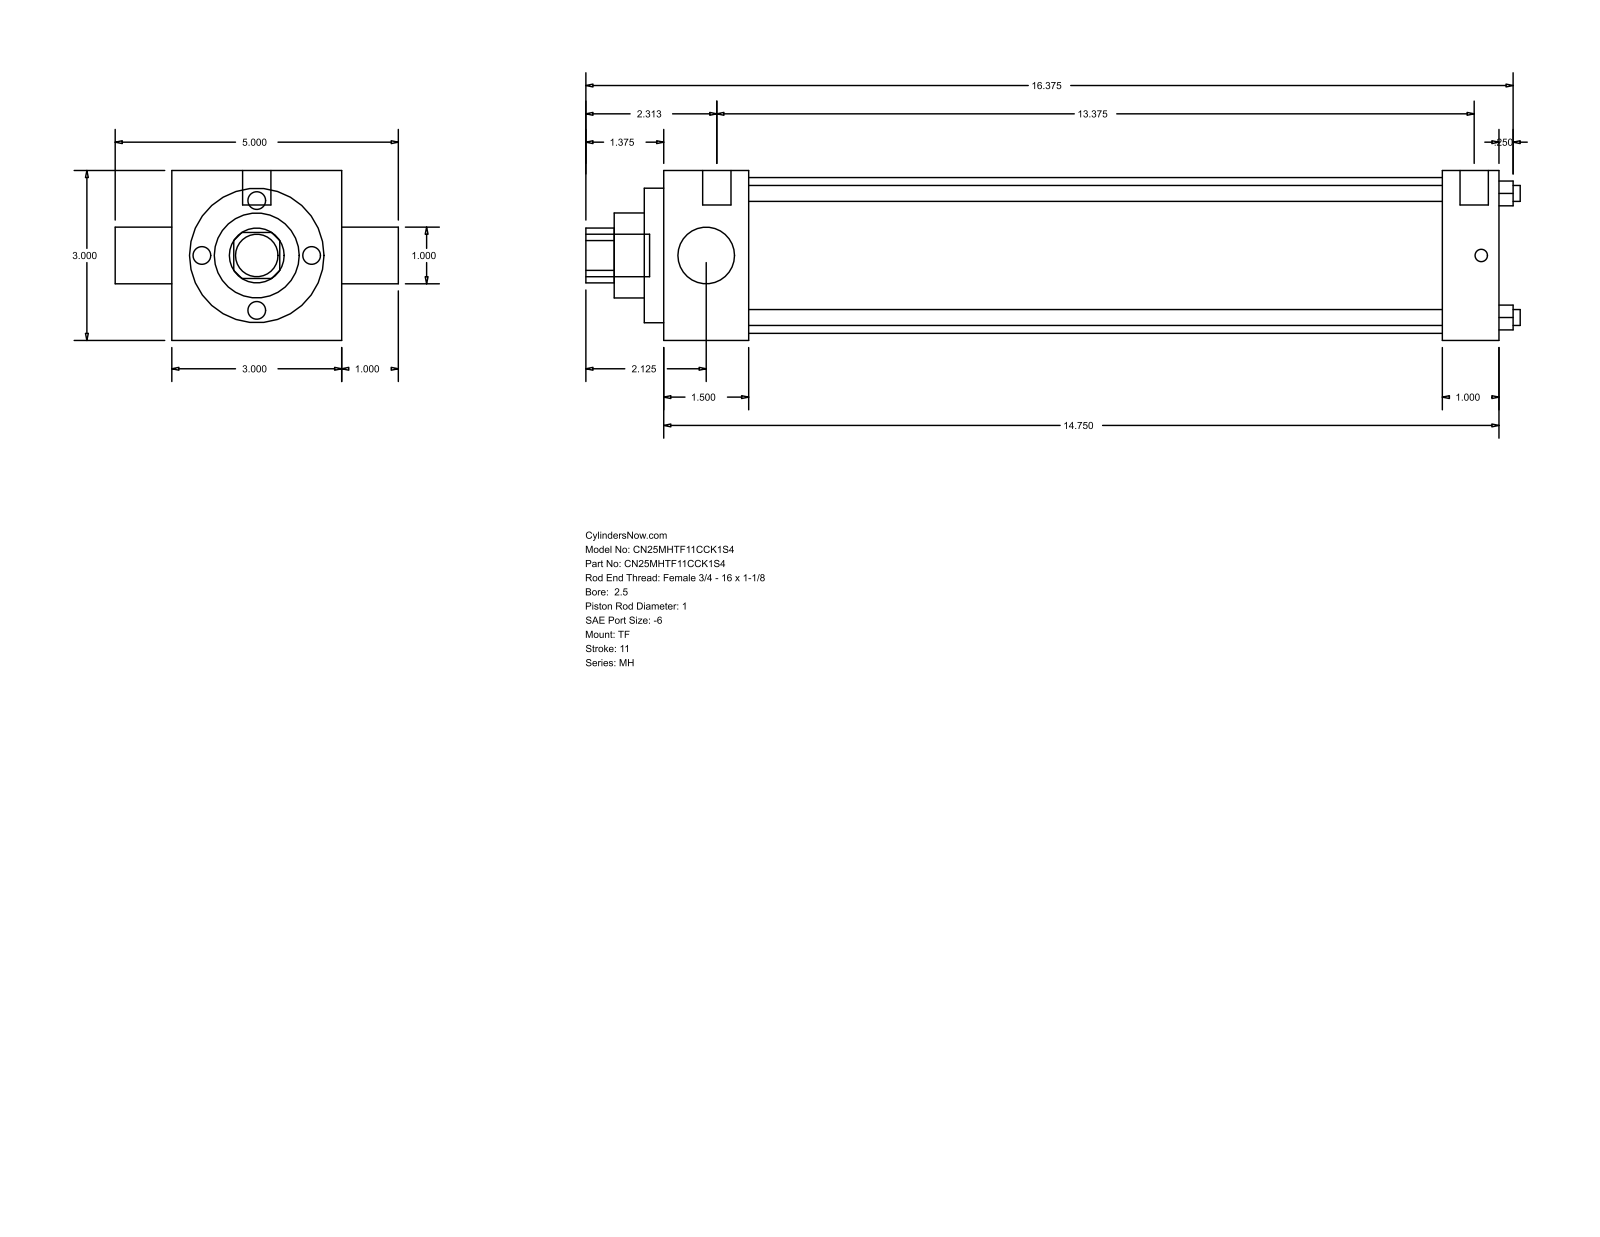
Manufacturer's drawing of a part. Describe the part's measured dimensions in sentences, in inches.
The part is named "MH_TF__0250_1". Its 3-D file was written by "GSSL Pune (CONFIG_CONTROL_DESIGN)". It is 0 solids with 86 faces: 61 planar, 25 cylindrical and 0 other. Overall it measures 16.5 by 5 by 3 inches. Round holes: 4 of diameter 0.281, 2 of diameter 1, 1 of diameter 1.5, 1 of diameter 2.375, 1 of diameter 2.75. Round bosses or shafts: 3 of diameter 0.219, 2 of diameter 0.5, 1 of diameter 0.75. Partial cylindrical surfaces (rounded edges, fillets, slot ends): 1 of radius 0.484. The main face-to-face distances are 3, 14.75, 1, 1.5, 13.25, 13.75, 12.25, 0.344, 1.844, 14.094. The hole center spacings are 1.548, 2.19, 3.097.
